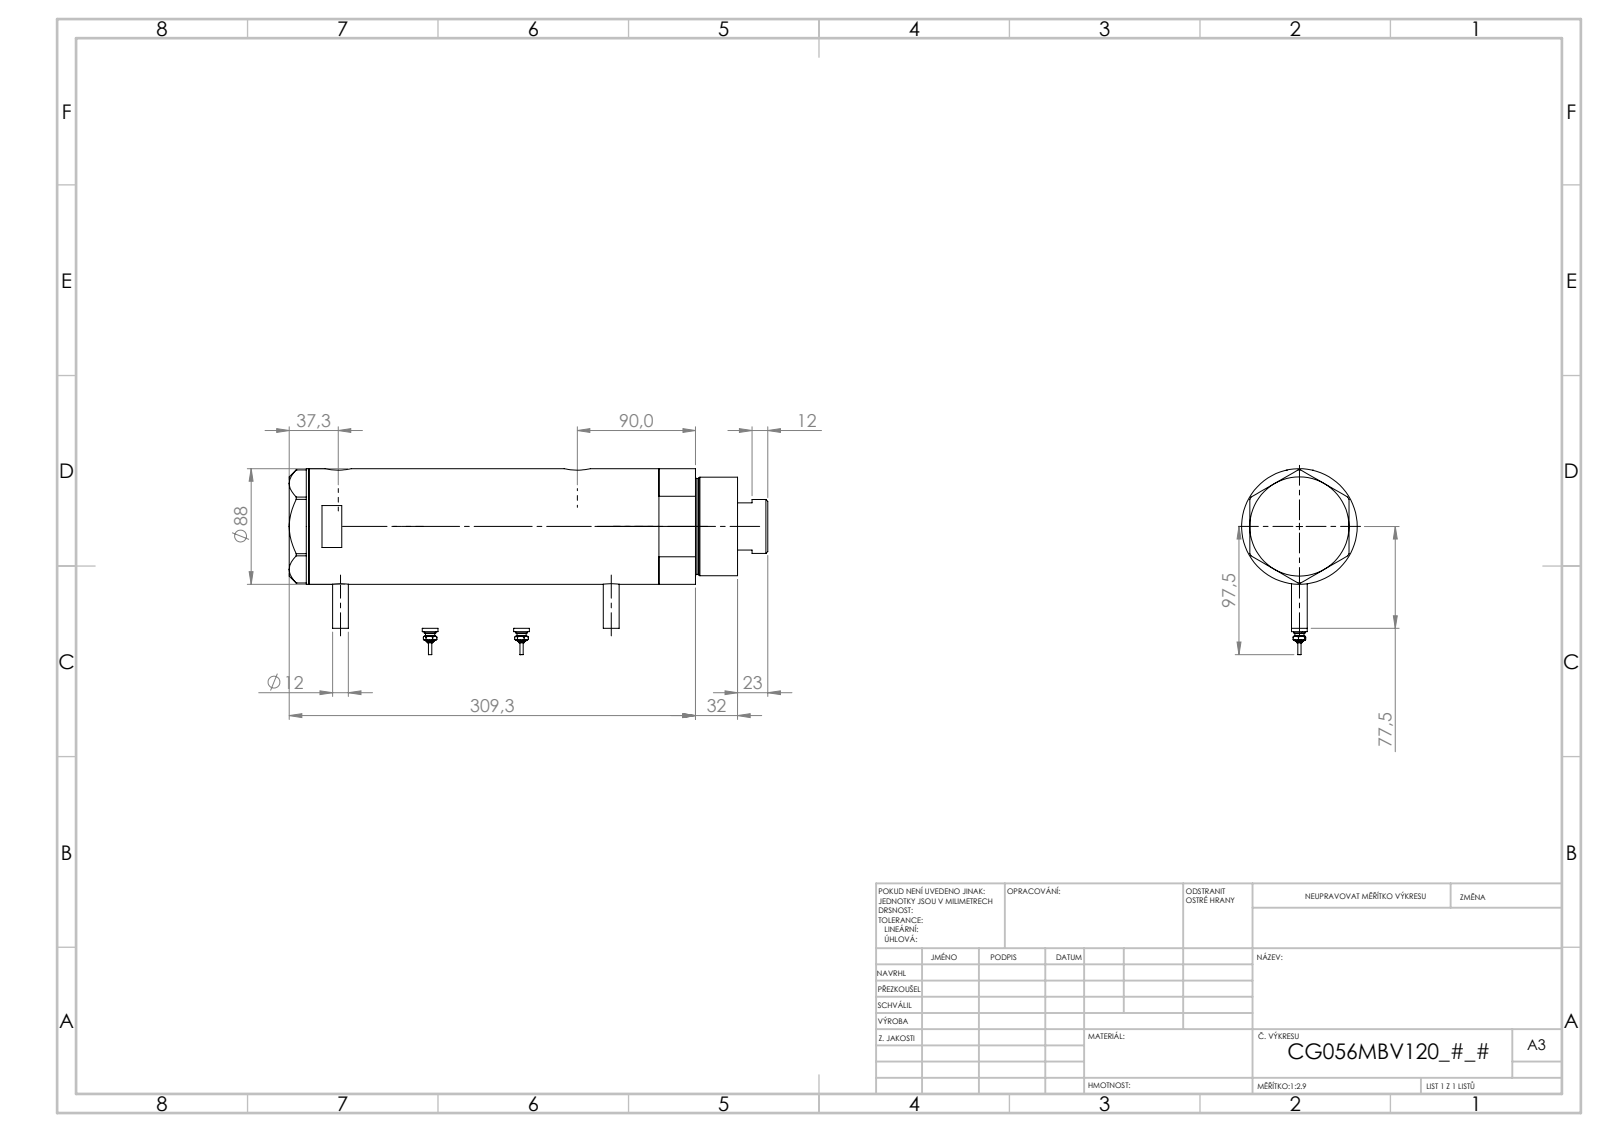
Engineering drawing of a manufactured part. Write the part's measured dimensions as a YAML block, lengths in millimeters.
part_name: "V270CG_VC; V270CG_MIDDLE; V270CG_SWITCH; V270CG_FRONT (+1 more)"
step_written_by: "SolidWorks 2019 (CONFIG_CONTROL_DESIGN)"
units: millimeters
bodies: {solids: 6, faces: 232, planar: 81, cylindrical: 77, other: 74}
overall_size: [344.47, 120.3, 88]
volume: 1765000
surface_area: 252327
round_holes:
  - {diameter: 5, count: 2}
  - {diameter: 12.5, count: 2}
  - {diameter: 13.16, count: 2}
  - {diameter: 20, count: 2}
  - {diameter: 14.5, count: 1}
  - {diameter: 42, count: 1}
  - {diameter: 43.5, count: 1}
  - {diameter: 56, count: 1}
  - {diameter: 60, count: 1}
  - {diameter: 80, count: 1}
round_bosses_or_shafts:
  - {diameter: 12, count: 2}
  - {diameter: 9, count: 2}
  - {diameter: 7, count: 2}
  - {diameter: 4.34, count: 2}
  - {diameter: 2.4, count: 2}
  - {diameter: 88, count: 1}
  - {diameter: 75, count: 1}
  - {diameter: 73, count: 1}
face_to_face_distances: [194.4, 26, 168.4, 15, 41, 209.4, 306.47, 321.47, 280.47, 112.07]
hole_center_spacings: [1.7, 25.8, 170.3, 172, 196.1, 197.8]
